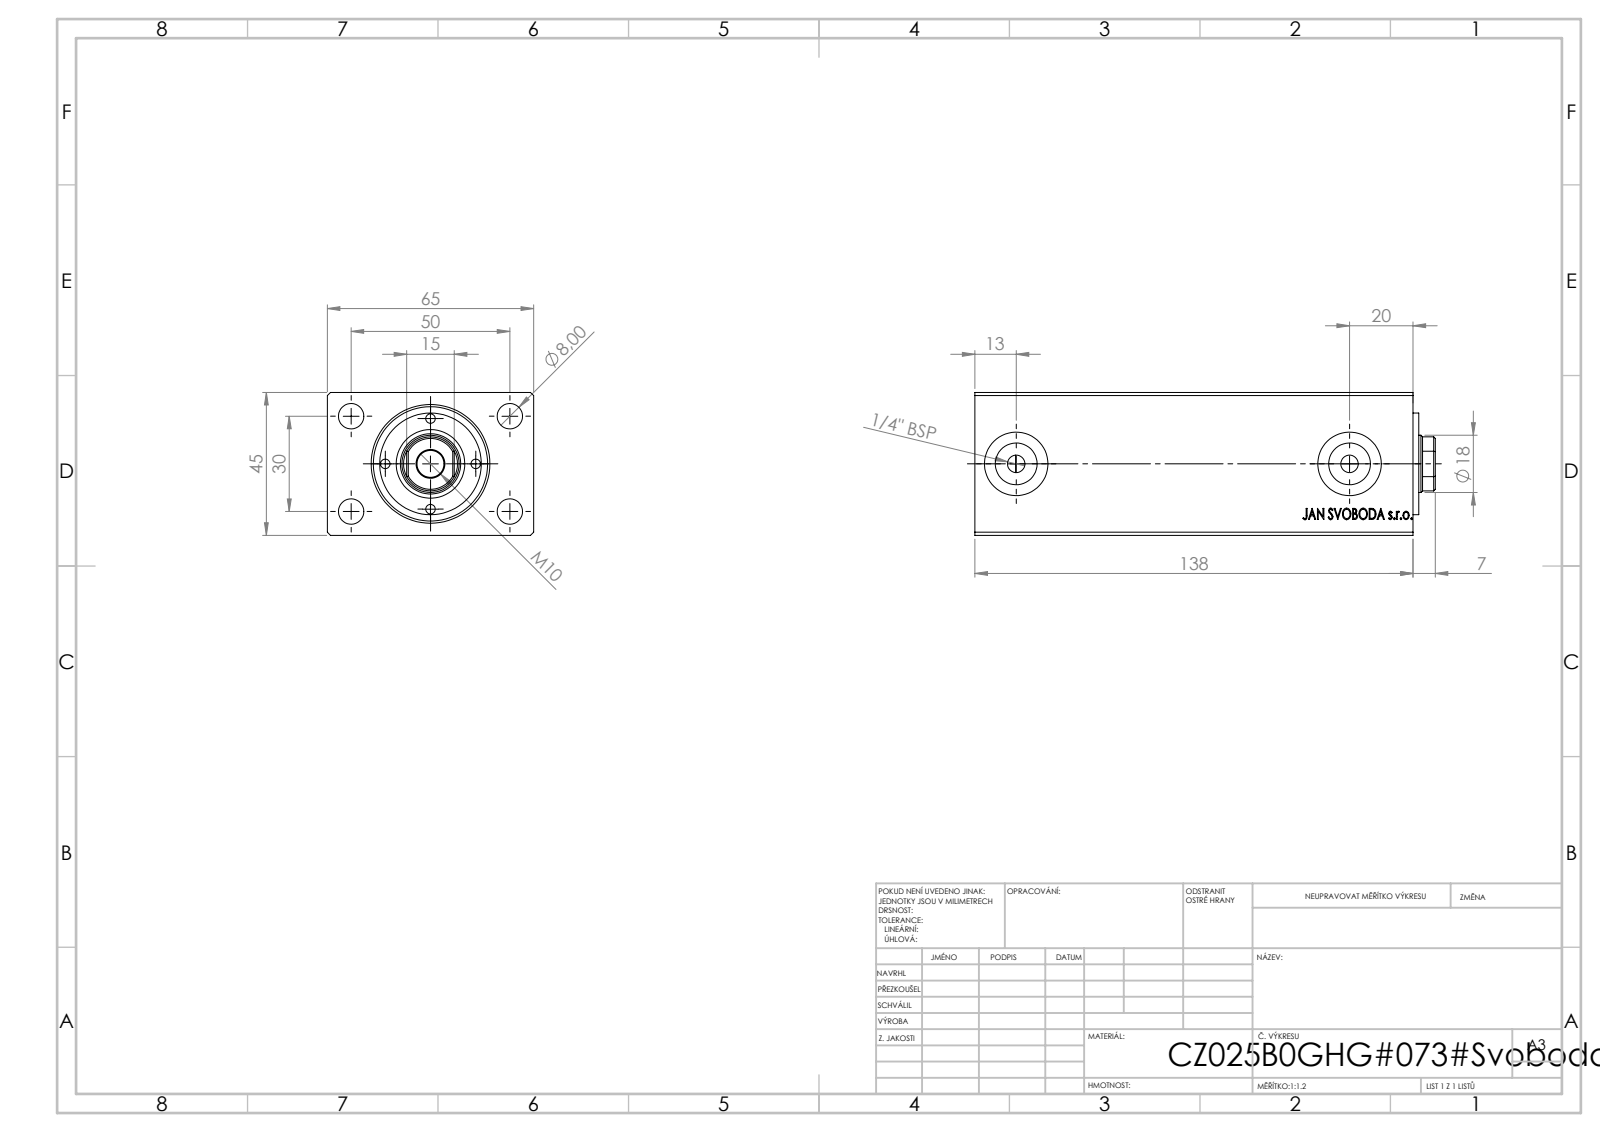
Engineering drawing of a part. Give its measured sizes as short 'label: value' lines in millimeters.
name: V500CZ_B_VC; V500CZ
written by: SolidWorks 2019 (CONFIG_CONTROL_DESIGN)
unit: mm
bodies: 3 solids, 873 faces (399 planar, 58 cylindrical, 416 other)
size: 145 × 65 × 45
volume: 371 858 mm³; area: 64 860 mm²
holes: 4× ⌀3, 4× ⌀8, 2× ⌀5.5, 2× ⌀13.16, 2× ⌀20, 1× ⌀8.5, 1× ⌀18, 1× ⌀19, 1× ⌀25, 1× ⌀36
bosses: 1× ⌀32
rounds: 1× R8.5
face distances: 45, 65, 138, 7, 137.8, 125.2, 12.6, 12.8, 1.8, 5.2
hole spacings: 14.25, 18.45, 20.15, 25.01, 29.15, 38.48, 42.02, 28.5
